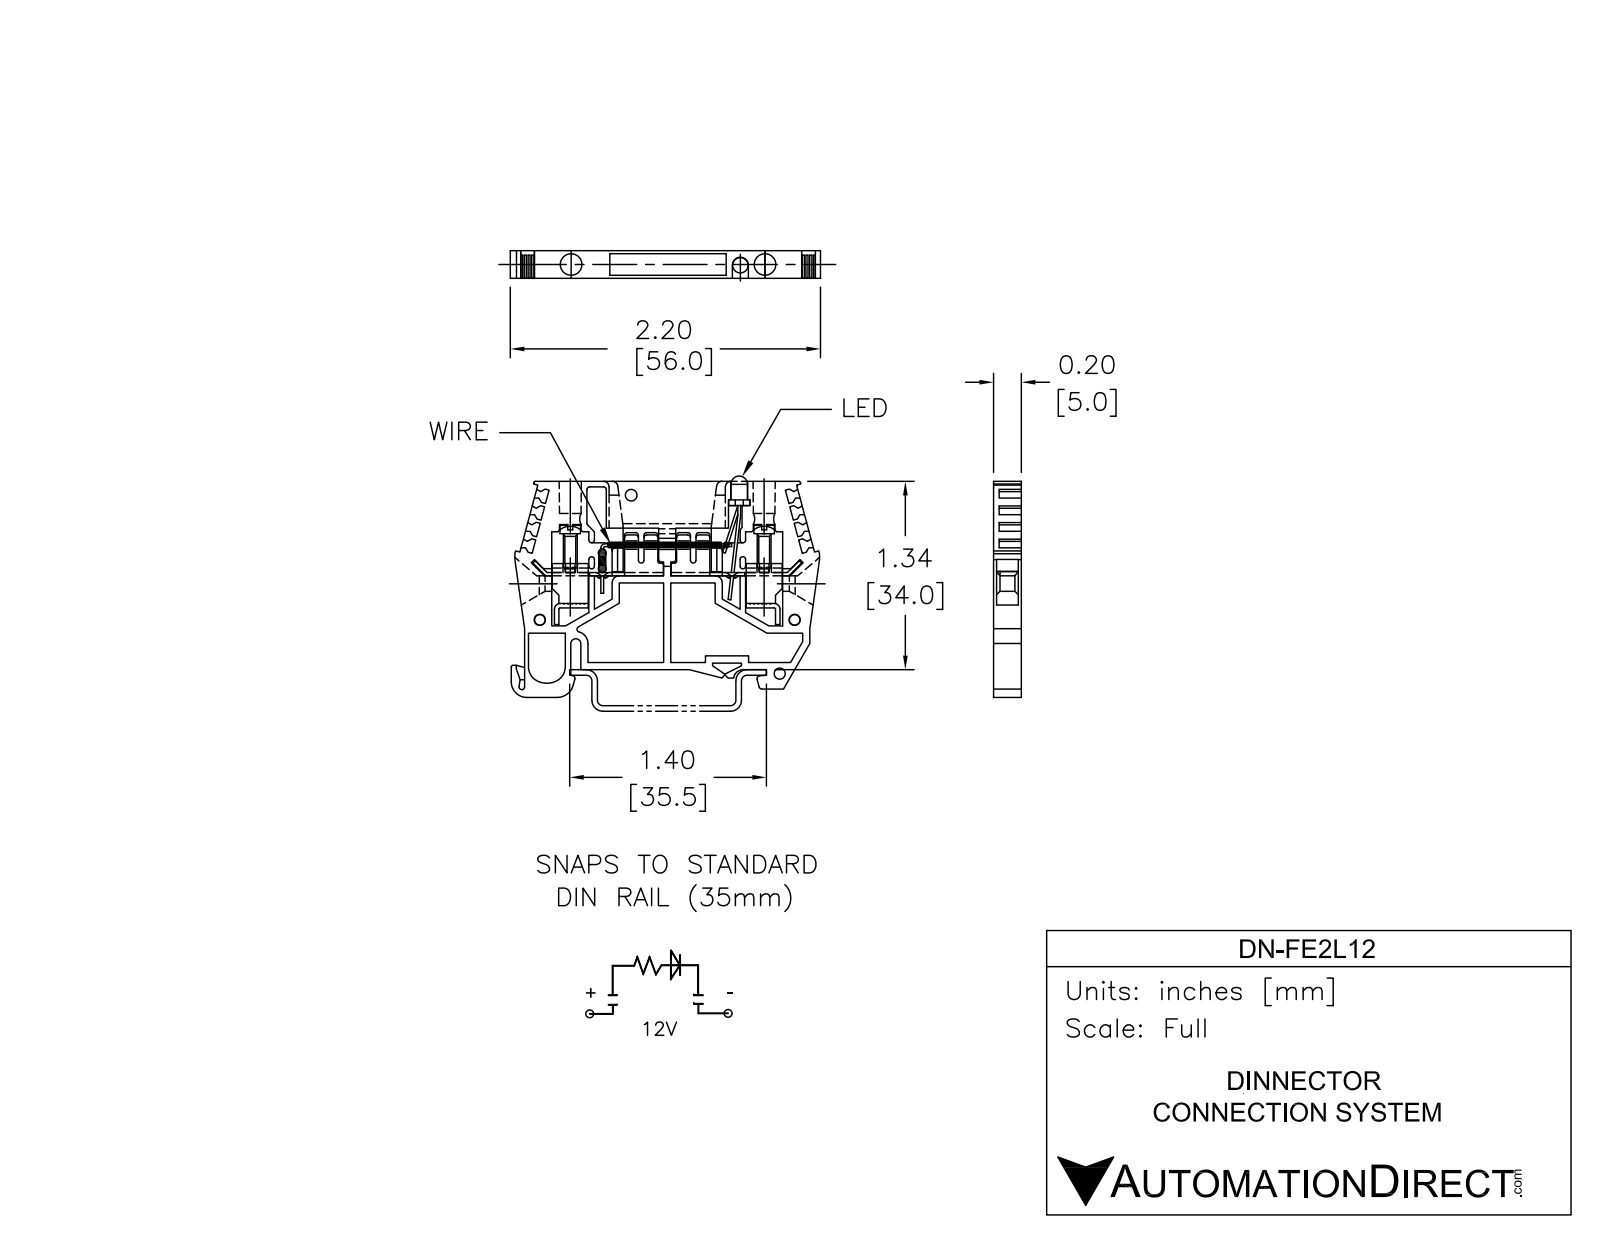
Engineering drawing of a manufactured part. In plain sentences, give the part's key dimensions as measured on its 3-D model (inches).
The part is named "20621; 4258000_DN-QFE2; 4358001_DN-FE2L12". Its 3-D file was written by "SolidWorks 2013 (AUTOMOTIVE_DESIGN)". It is 2 solids with 326 faces: 199 planar, 86 cylindrical and 41 other. Overall it measures 2.191 by 1.559 by 0.197 inches. Its volume is 0.459 cubic inches and its surface area 9.325 square inches. Round holes: 3 of diameter 0.079, 2 of diameter 0.161. Round bosses or shafts: 10 of diameter 0.012, 1 of diameter 0.157, 1 of diameter 0.118. Partial cylindrical surfaces (rounded edges, fillets, slot ends): 11 of radius 0.02, 5 of radius 0.118, 3 of radius 0.039, 1 of radius 0.035, 1 of radius 0.041, 1 of radius 0.067, 1 of radius 0.077, 1 of radius 0.11. The main face-to-face distances are 0.197, 1.339, 0.087, 0.175, 0.022, 0.039, 0.122, 0.136, 0.142, 0.055. The hole center spacings are 0.396, 1.378, 1.747, 1.811.
